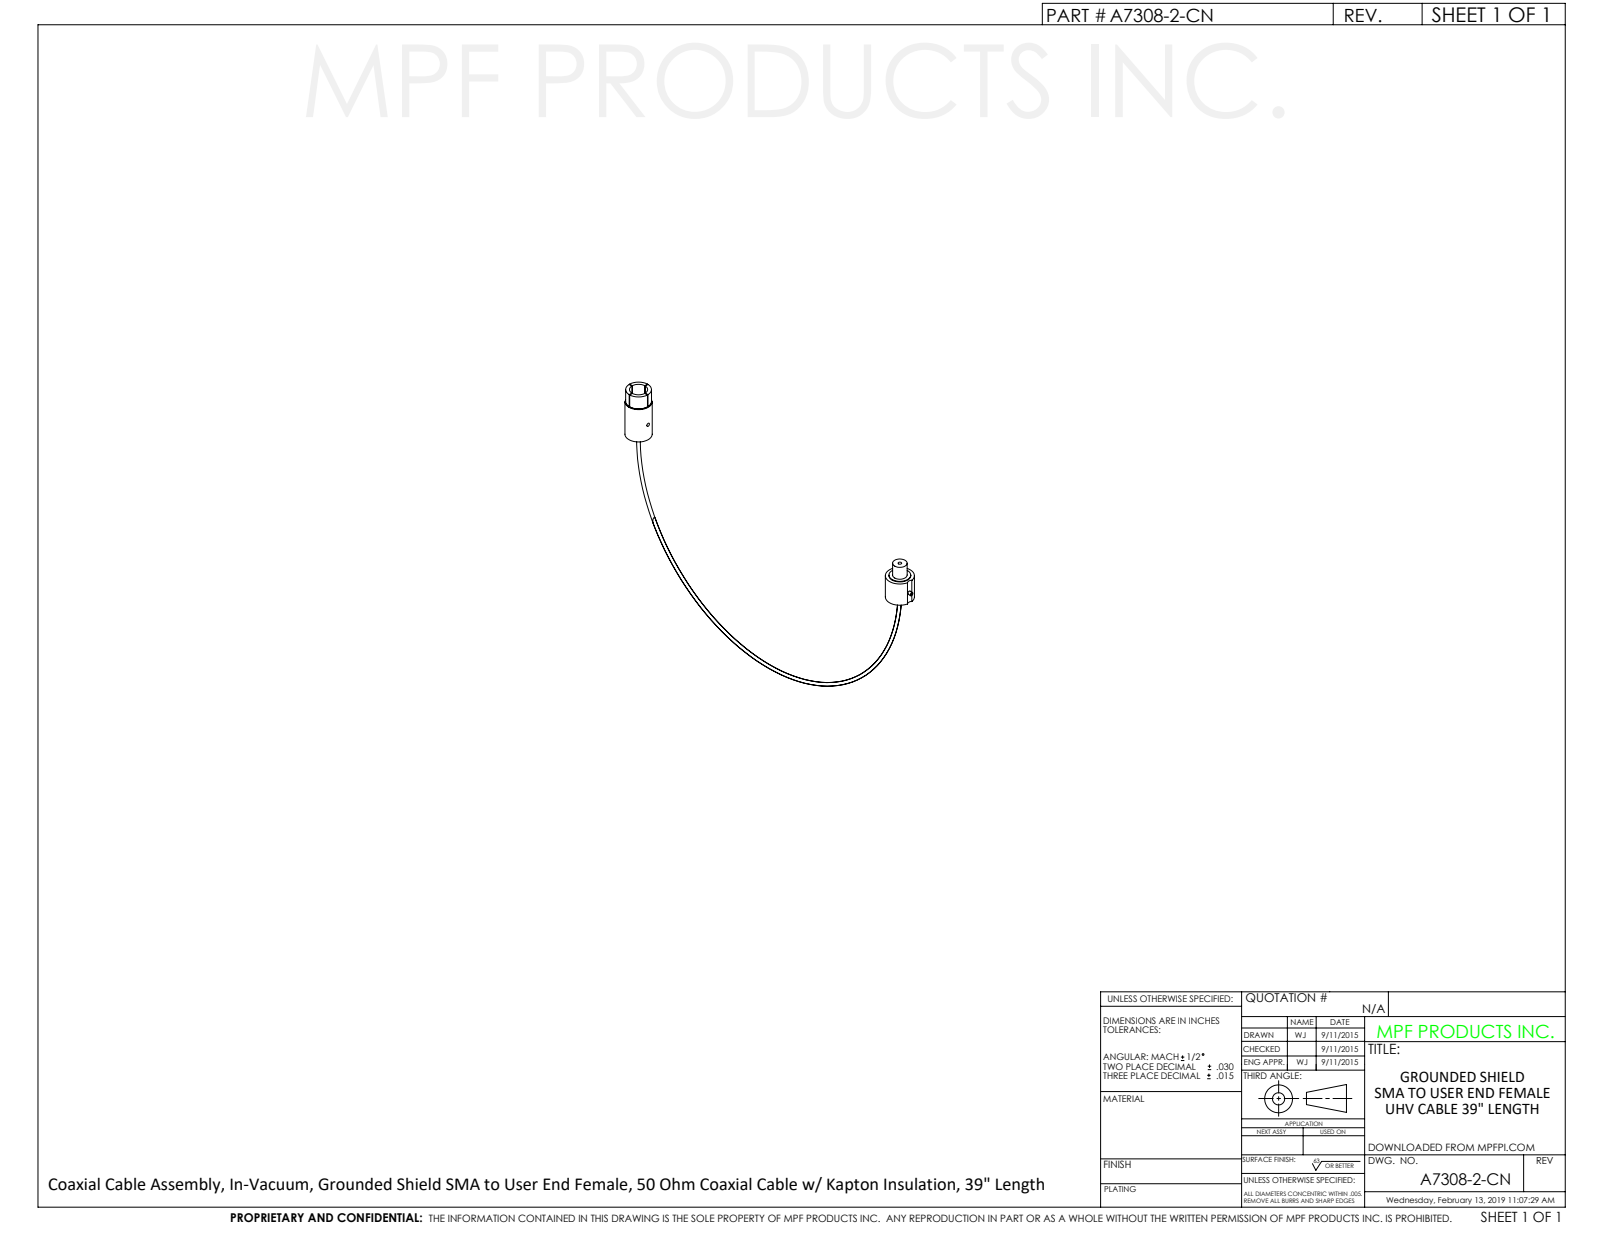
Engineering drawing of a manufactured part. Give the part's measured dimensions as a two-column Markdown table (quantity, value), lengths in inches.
| quantity | value |
| --- | --- |
| part name | A7307-2-CN |
| STEP written by | SolidWorks 2012 (CONFIG_CONTROL_DESIGN) |
| units | inches |
| bodies | 1 solid, 58 faces (25 planar, 28 cylindrical, 5 other) |
| overall size | 10.993 × 6.833 × 0.8 |
| volume | 0.92 in³ |
| surface area | 15.18 in² |
| round holes (diameter × count) | 0.1 × 3, 0.025 × 1, 0.5 × 1 |
| round bosses / shafts (diameter × count) | 0.8 × 1, 0.75 × 1, 0.71 × 1, 0.6 × 1, 0.4 × 1, 0.11 × 1, 0.101 × 1 |
| partial cylindrical surfaces (radius × count) | 0.138 × 1 |
| main face-to-face distances | 0.398, 0.714, 0.315, 1.898, 1.5, 1.185, 0.598, 0.2, 0.115, 1.3 |
| hole center spacings | 0.578, 10.162 |
